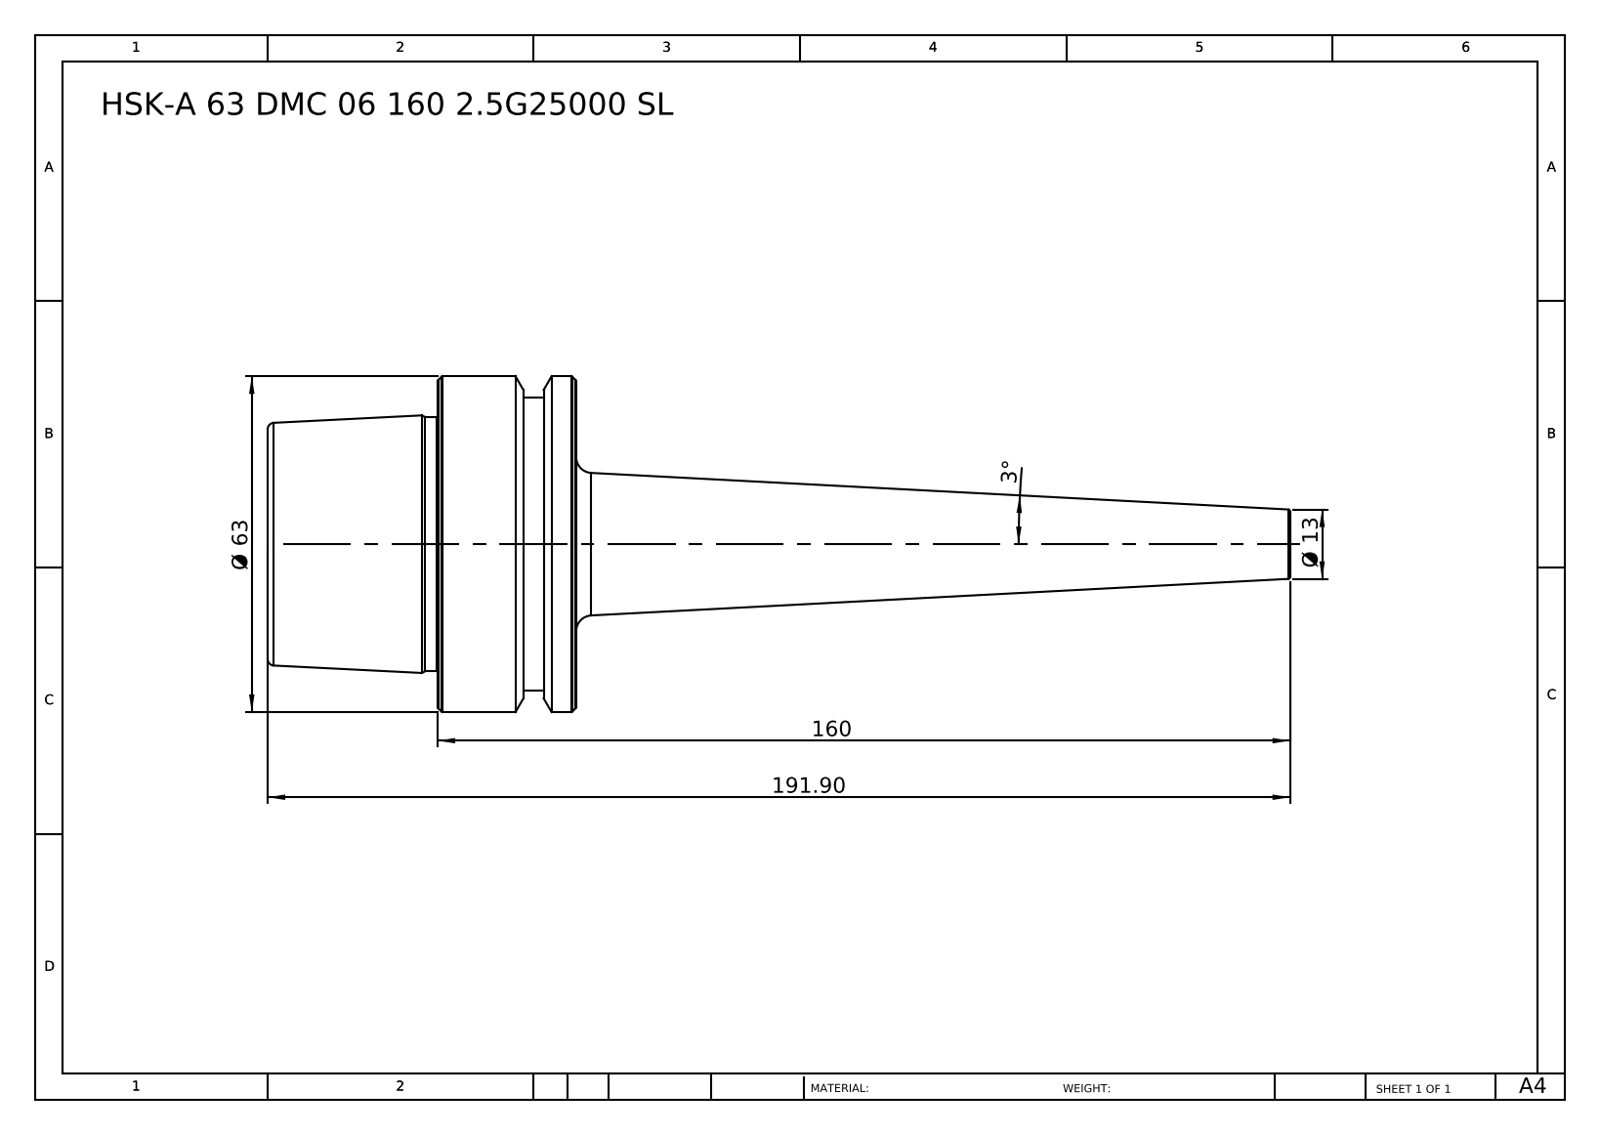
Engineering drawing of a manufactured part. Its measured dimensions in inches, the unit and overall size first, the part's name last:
Units: inches
Overall size (bounding box): 7.555 × 2.48 × 2.48
Round bosses / shafts (diameter × count): ⌀2.48 ×1, ⌀2.165 ×1, ⌀1.881 ×1
Main face-to-face distances: 2.28, 1.024, 1.256, 0.24, 0.783, 2.039, 0.39, 0.15, 0.634, 1.89
Volume: 10.78 in³ · Surface area: 38.05 in²
Bodies: 1 solid, 46 faces (6 planar, 8 cylindrical, 32 other)
Part name (STEP PRODUCT): HSK-A 63 DMC 06 160 2.5G25000 SL
STEP written by: SolidWorks 2014 (CONFIG_CONTROL_DESIGN)
